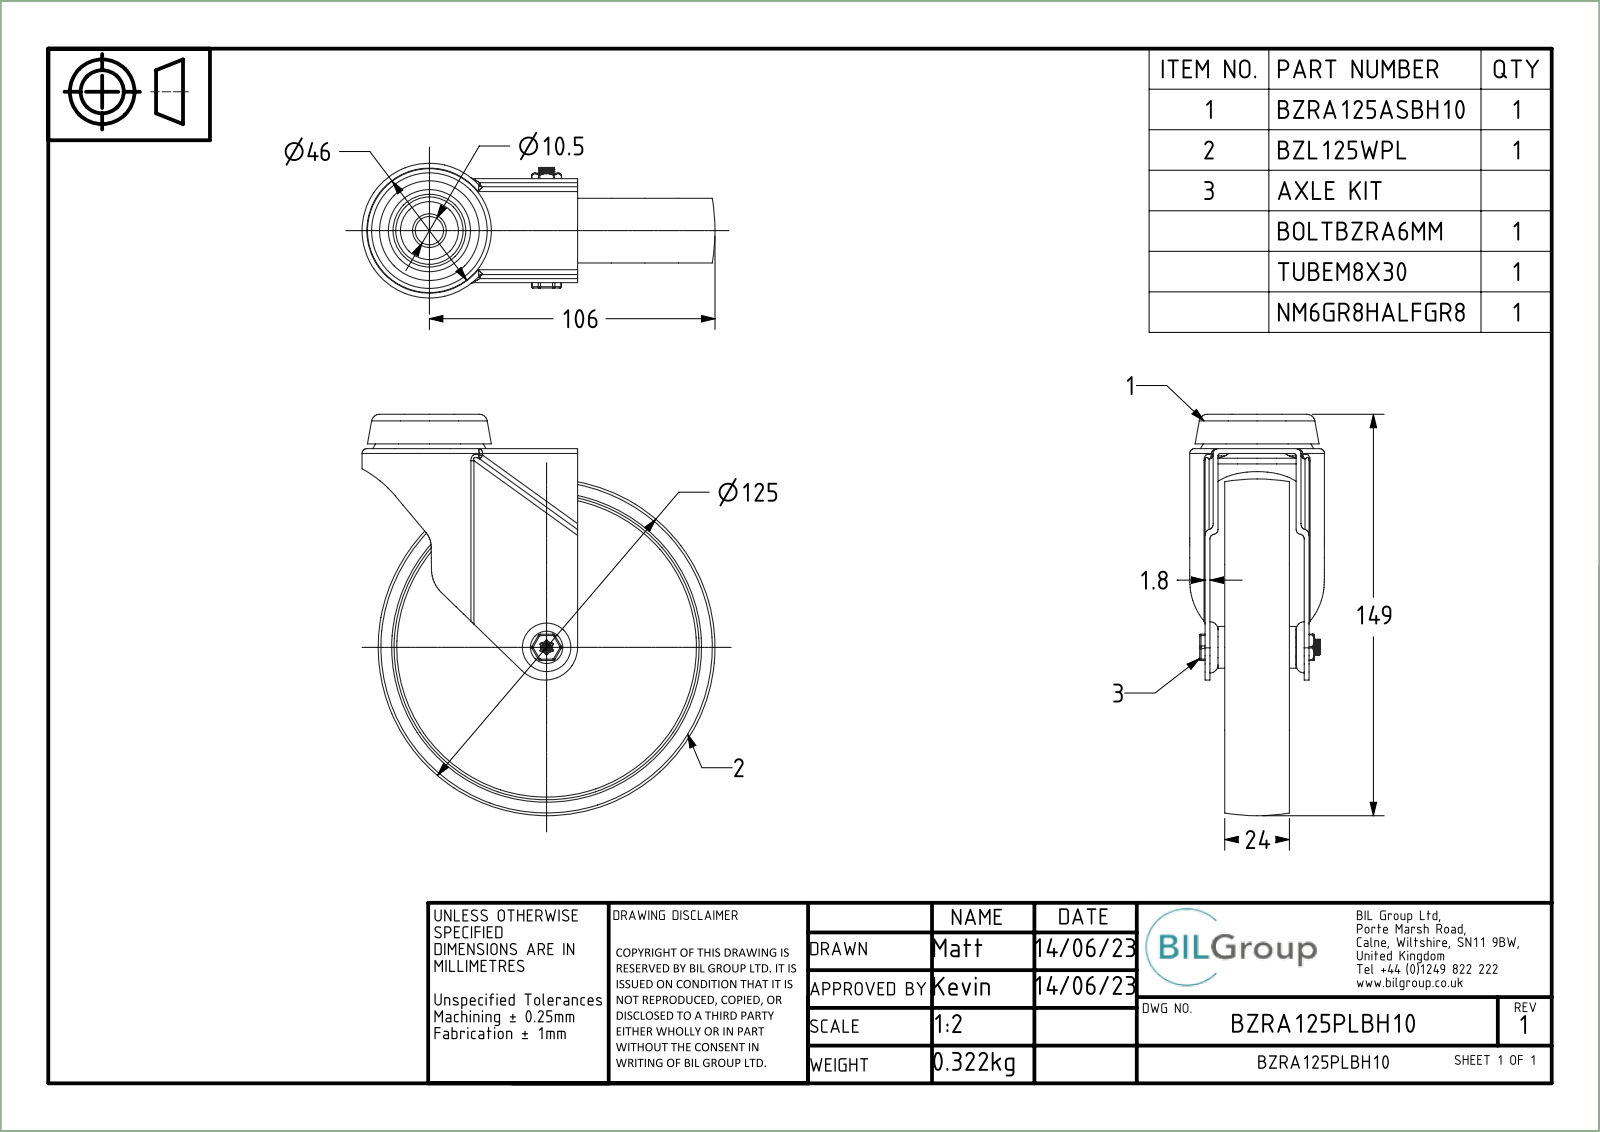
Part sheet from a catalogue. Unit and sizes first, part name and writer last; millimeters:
Units: millimetres
Overall size (bounding box): 149 × 130 × 50
Round holes (diameter × count): ⌀6 ×1, ⌀6.3 ×1, ⌀6.4 ×1, ⌀8.2 ×1, ⌀8.3 ×1, ⌀10.5 ×1, ⌀10.56 ×1, ⌀28 ×1
Round bosses / shafts (diameter × count): ⌀39 ×1, ⌀18 ×1, ⌀15.5 ×1, ⌀14.76 ×1, ⌀8 ×1, ⌀7.95 ×1, ⌀5 ×1
Partial cylindrical surfaces — rounded edges, fillets, slot ends (radius × count): R1 ×18, R1.8 ×14, R0.5 ×12, R0.4 ×6, R0.9 ×6, R2.12 ×1, R8 ×1, R12 ×1
Main face-to-face distances: 6, 1.8, 16.3, 22.3, 3, 33.8, 9, 29.5, 36.8, 14.5
Volume: 146 444 mm³ · Surface area: 76 944 mm²
Bodies: 6 solids, 379 faces (59 planar, 169 cylindrical, 151 other)
Part name (STEP PRODUCT): BZRA125ASBH10; ZINC PLATED PRESSED STEEL FORKS; ZINC PLATED PRESSED STEEL HEAD; BZRA125PLBH10 (+8 more)
STEP written by: Spatial InterOp 3D (CONFIG_CONTROL_DESIGN)
